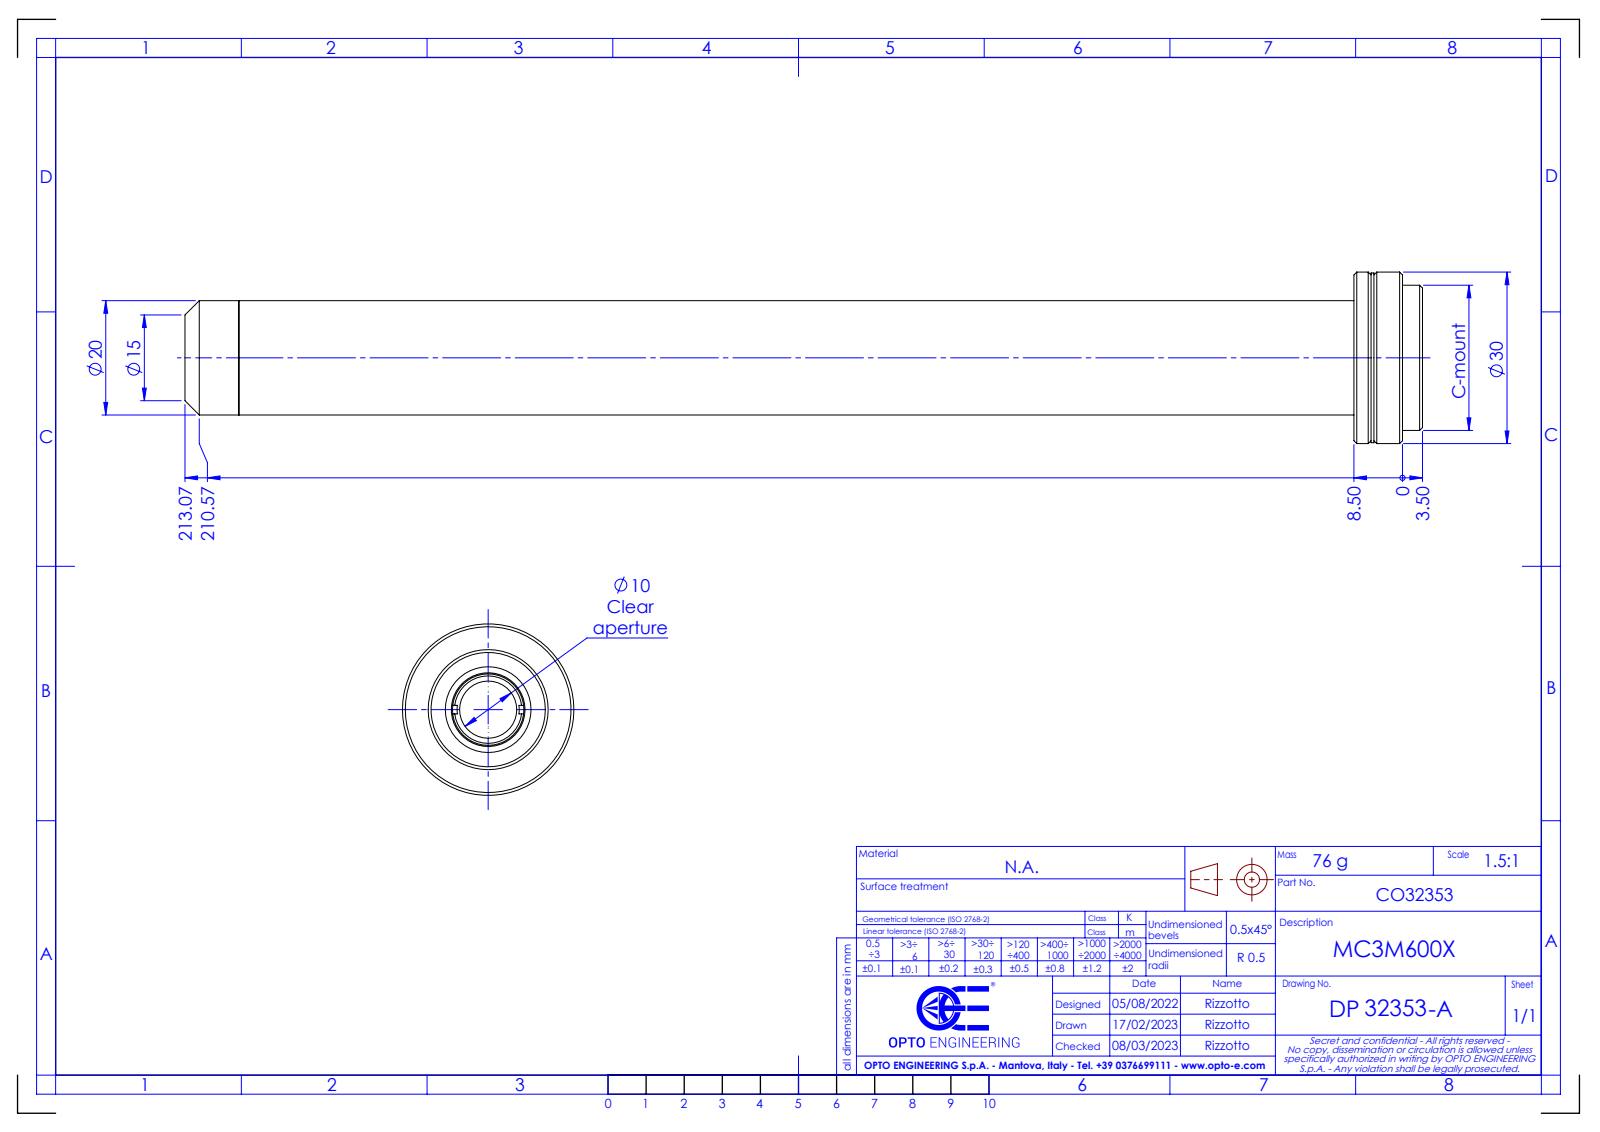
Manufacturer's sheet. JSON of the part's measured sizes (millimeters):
{"part_name": "DP32353-A_MC3M600X", "step_written_by": "SolidWorks 2021 (CONFIG_CONTROL_DESIGN)", "units": "millimeters", "bodies": {"solids": 0, "faces": 64, "planar": 16, "cylindrical": 22, "other": 26}, "overall_size": [216.56, 30, 30], "round_holes": [[10, 1], [12.5, 1], [17.5, 1], [18, 1]], "round_bosses_or_shafts": [[30, 1], [29.7, 1], [25.4, 1], [20, 1]], "face_to_face_distances": [8.5, 3.5, 5, 3, 0.5, 5.5, 12, 9, 195.14, 198.14]}
